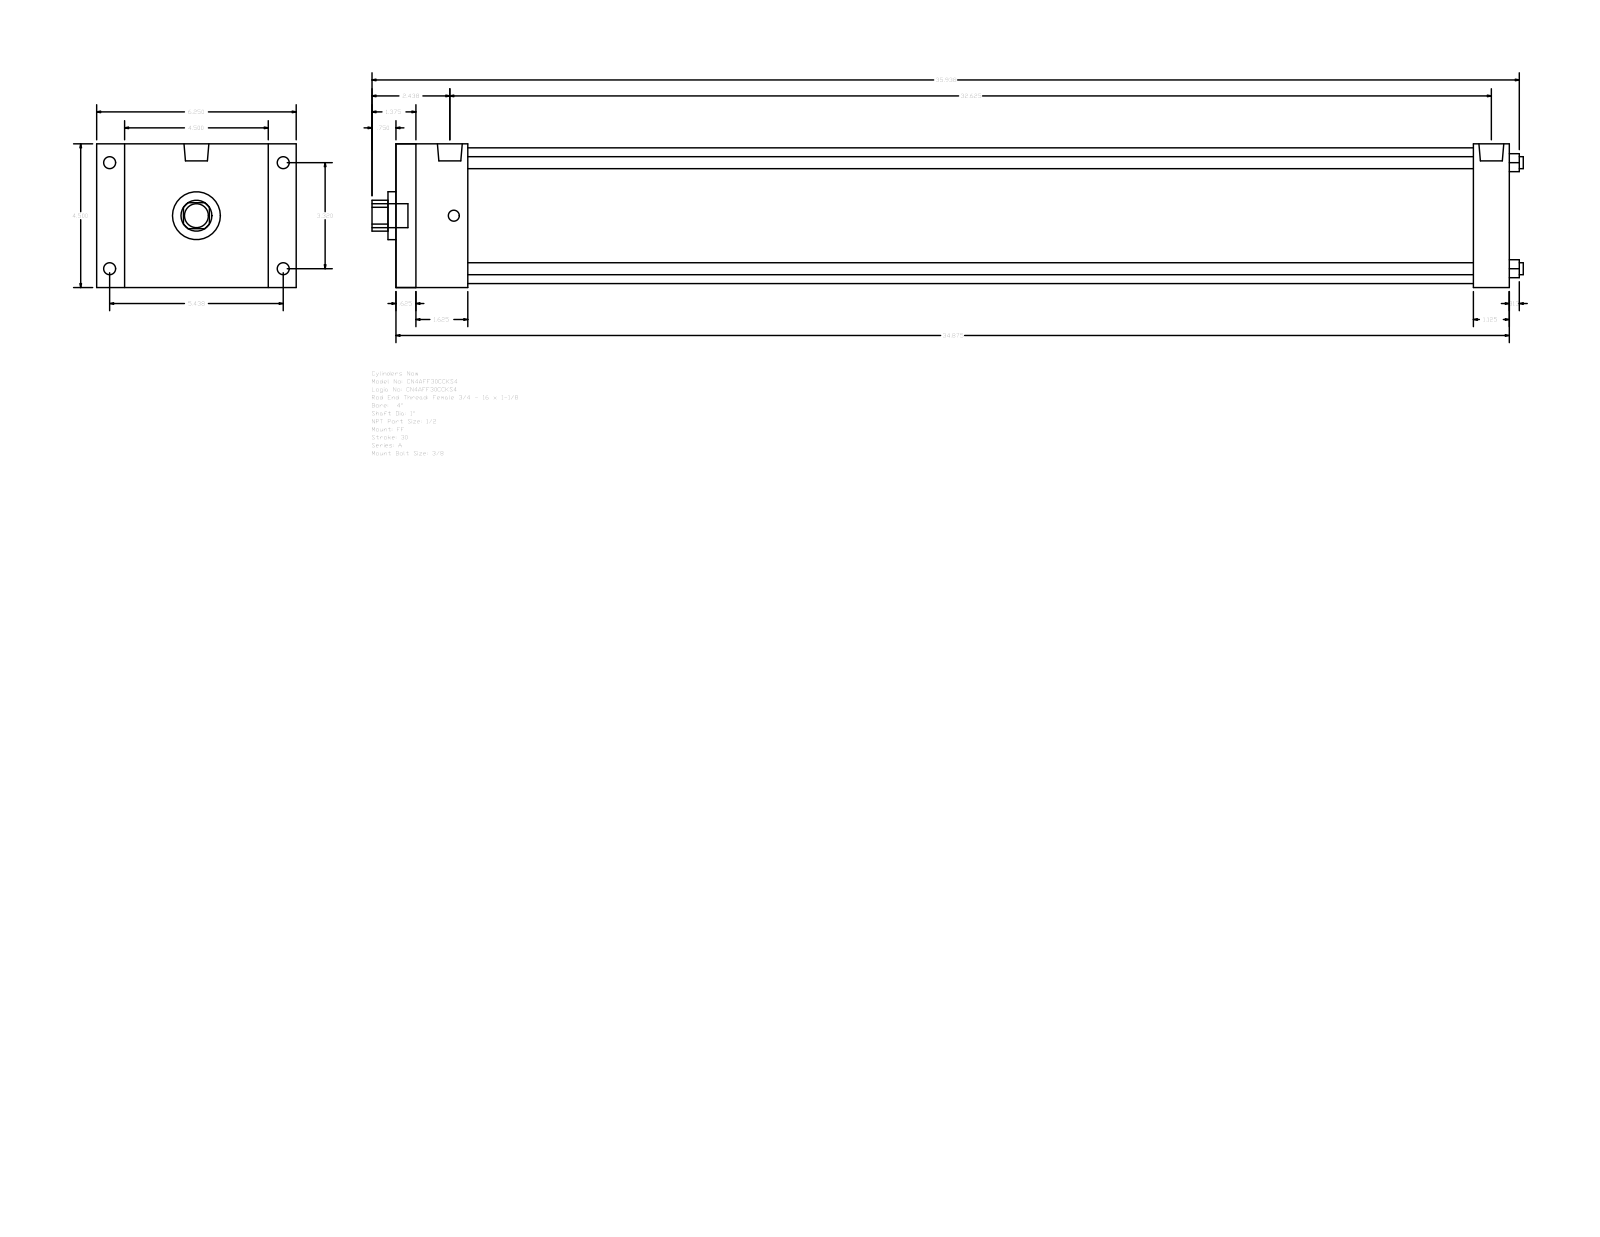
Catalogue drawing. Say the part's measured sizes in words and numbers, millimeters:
The part is named "A_FF__0400_1". Its 3-D file was written by "GSSL Pune (CONFIG_CONTROL_DESIGN)". It is 0 solids with 92 faces: 64 planar, 28 cylindrical and 0 other. Overall it measures 915.99 by 158.75 by 114.3 millimeters. Round holes: 4 of diameter 9.53, 1 of diameter 25.4, 1 of diameter 38.1, 1 of diameter 107.95. Round bosses or shafts: 4 of diameter 9.53, 4 of diameter 8.73, 2 of diameter 19.77, 1 of diameter 19.05. Partial cylindrical surfaces (rounded edges, fillets, slot ends): 1 of radius 12.29. The main face-to-face distances are 114.3, 885.83, 15.87, 869.96, 22.23, 136.53, 857.25, 841.38, 28.58, 57.15. The hole center spacings are 59.62, 84.32, 119.25.
